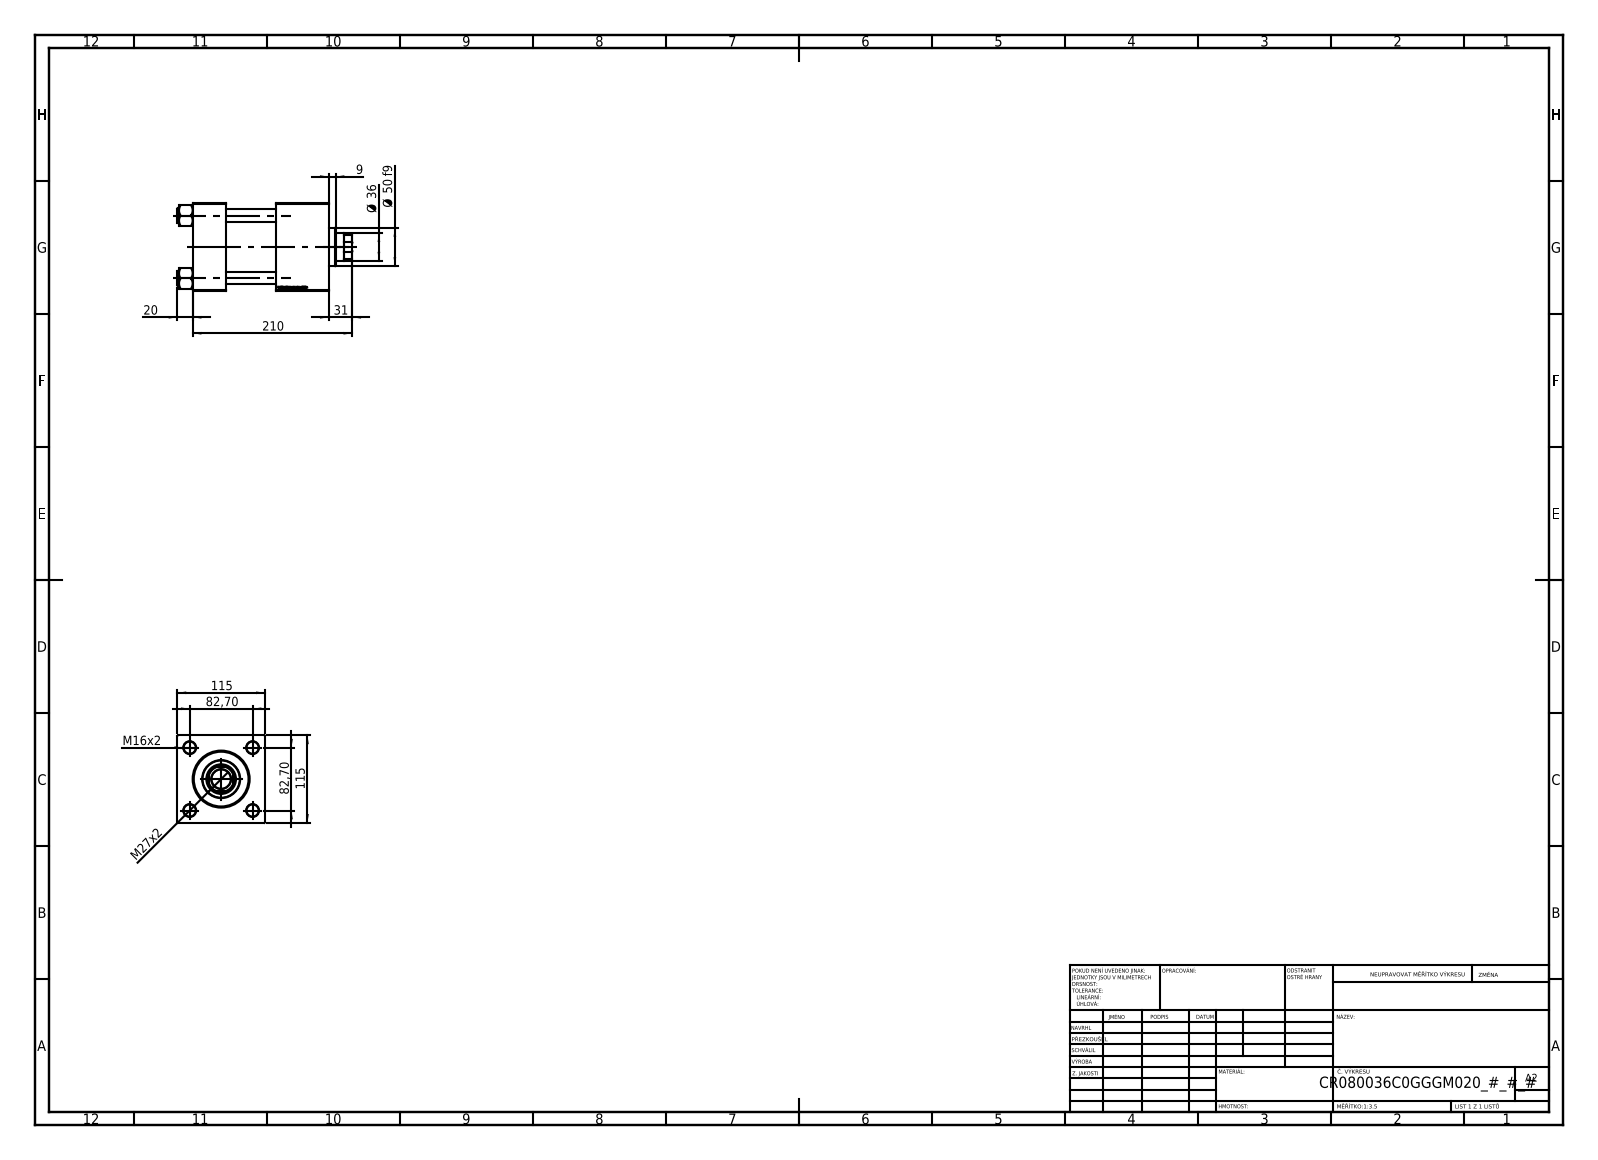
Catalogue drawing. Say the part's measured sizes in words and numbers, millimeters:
The part is named "NUT_M5_C; V215CR_C_TYCINKA; V215_VC_A; V215CR_VCP_C (+1 more)". Its 3-D file was written by "SolidWorks 2019 (CONFIG_CONTROL_DESIGN)". It is 11 solids with 1197 faces: 574 planar, 87 cylindrical and 536 other. Overall it measures 230 by 115 by 115 millimeters. Its volume is 1 786 000 cubic millimeters and its surface area 268 442 square millimeters. Round holes: 4 of diameter 16, 2 of diameter 7, 2 of diameter 26.44, 2 of diameter 35, 1 of diameter 25.5, 1 of diameter 36, 1 of diameter 39, 1 of diameter 61, 1 of diameter 72, 1 of diameter 80. Round bosses or shafts: 4 of diameter 19, 1 of diameter 86, 1 of diameter 50. Partial cylindrical surfaces (rounded edges, fillets, slot ends): 1 of radius 17.5. The main face-to-face distances are 115, 44, 179, 135, 110, 69, 66, 20, 150.3, 106.3. The hole center spacings are 58.48, 82.7, 116.96, 111.
